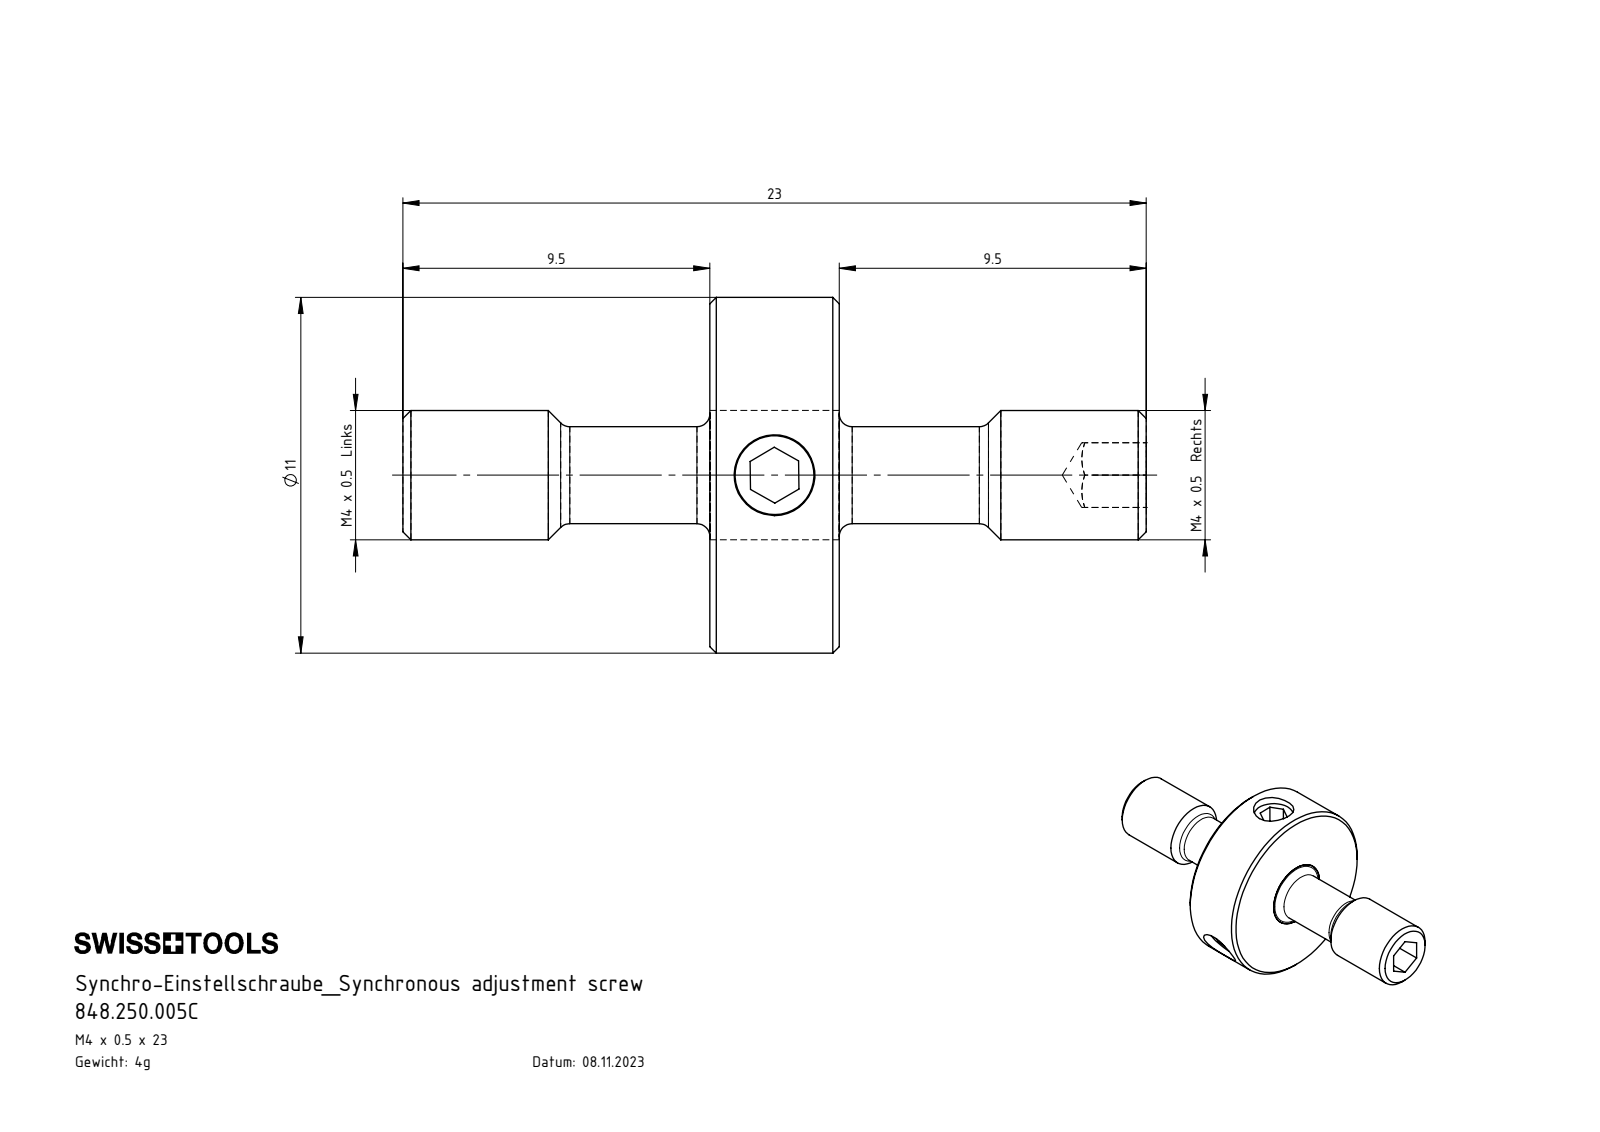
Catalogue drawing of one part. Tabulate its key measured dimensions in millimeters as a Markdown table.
| quantity | value |
| --- | --- |
| part name | Z25-ER3.001.023_A; 848.250.005C; Z25-ER3.002.004_A; ISO 4026 - M3 x 3 |
| STEP written by | SolidWorks 2022 (AUTOMOTIVE_DESIGN) |
| units | millimeters |
| bodies | 5 solids, 99 faces (39 planar, 26 cylindrical, 34 other) |
| overall size | 23 × 11 × 11 |
| volume | 553 mm³ |
| surface area | 853 mm² |
| round holes (diameter × count) | 2.5 × 3 |
| round bosses / shafts (diameter × count) | 3 × 4, 11 × 1, 4 × 1 |
| main face-to-face distances | 4, 9.5, 13.5, 1.5, 2, 3, 10.75, 12.25, 1.25, 2.75 |
